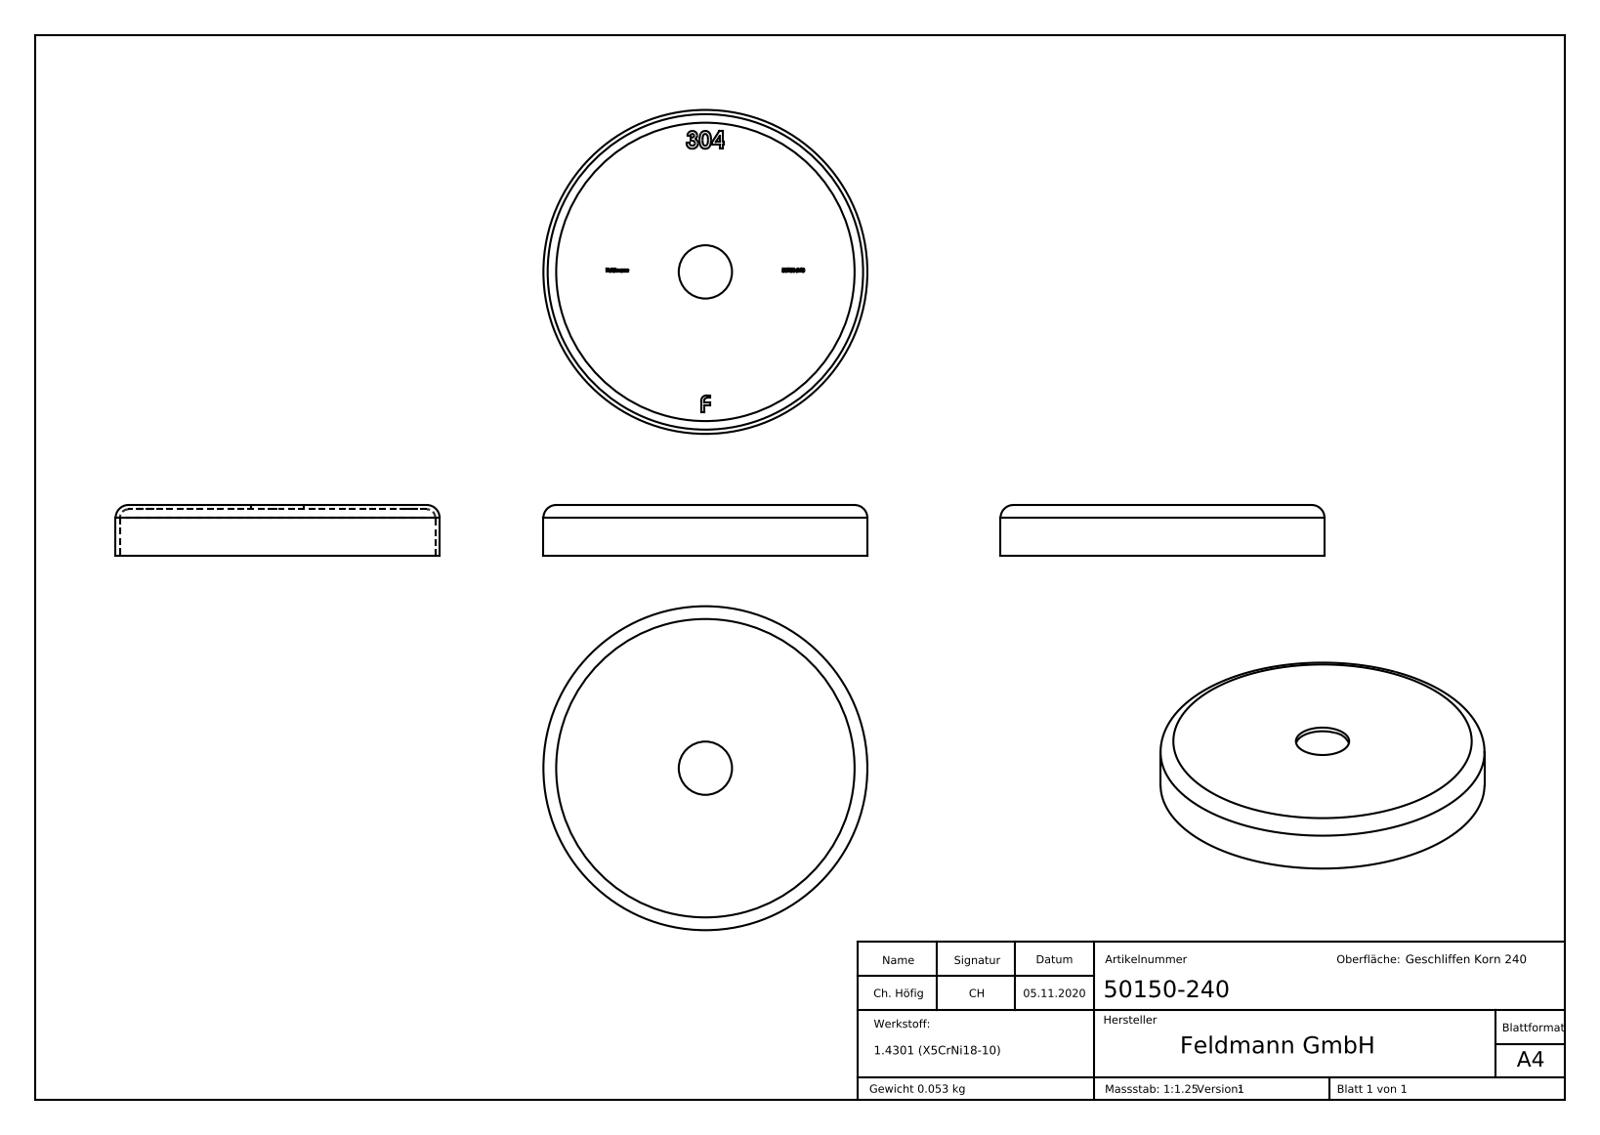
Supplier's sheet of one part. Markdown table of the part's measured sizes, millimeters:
| quantity | value |
| --- | --- |
| part name | 50150-240 |
| STEP written by | SolidWorks 2018 (CONFIG_CONTROL_DESIGN) |
| units | millimeters |
| bodies | 1 solid, 287 faces (155 planar, 6 cylindrical, 126 other) |
| overall size | 76 × 76 × 12 |
| volume | 6 747 mm³ |
| surface area | 13 789 mm² |
| round holes (diameter × count) | 12.5 × 1, 74 × 1 |
| round bosses / shafts (diameter × count) | 76 × 1 |
| main face-to-face distances | 1, 11, 12, 11.1, 0.9, 0.71, 5, 4.29, 0.58, 0.69 |
